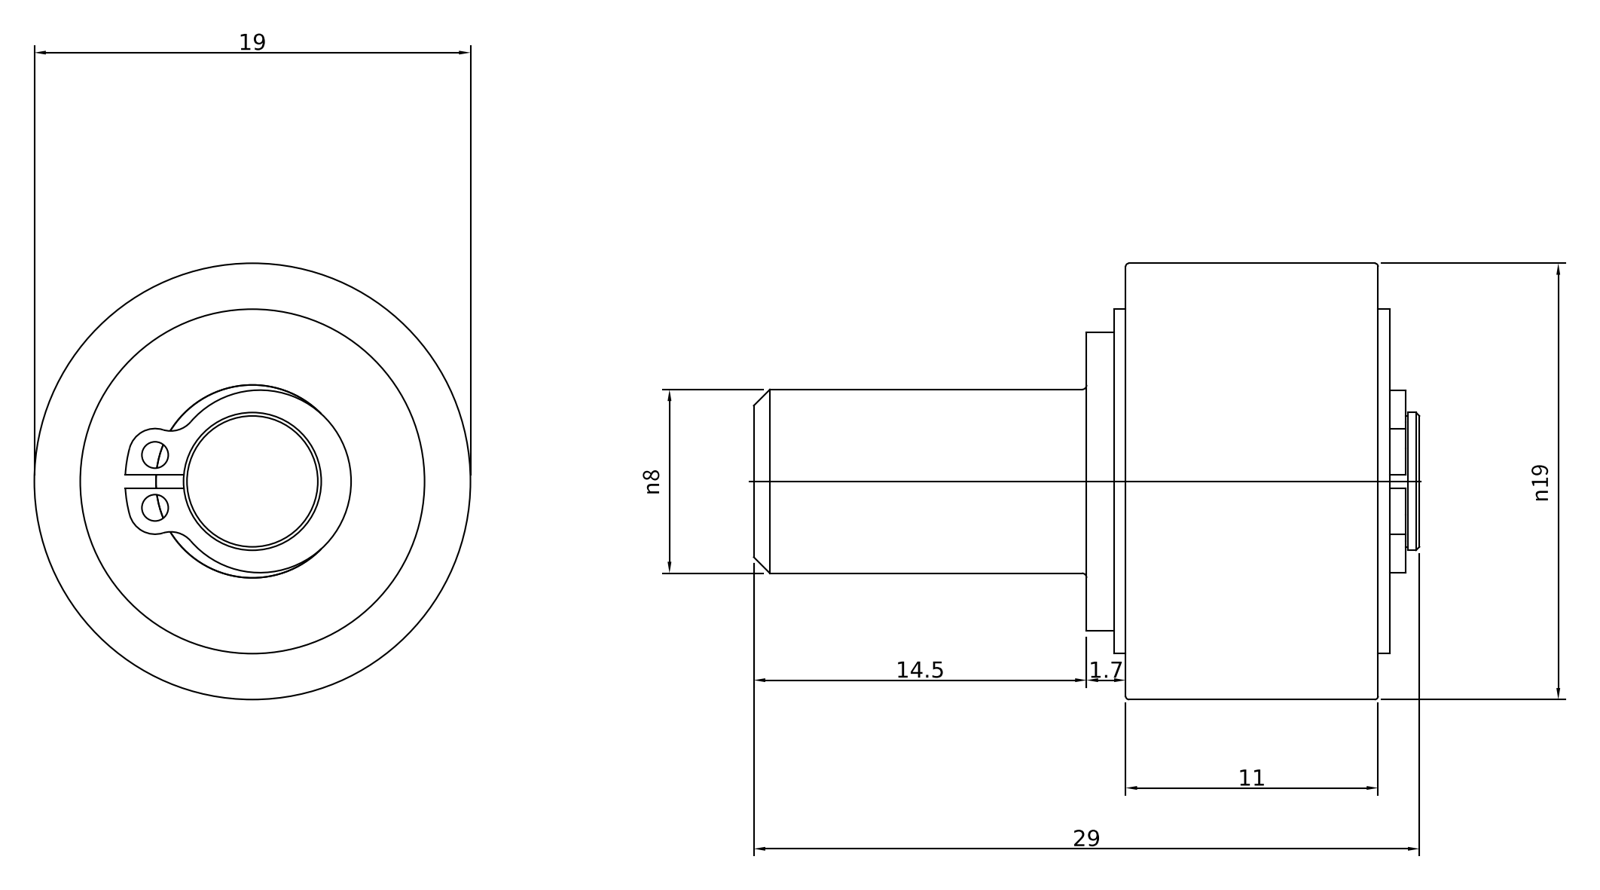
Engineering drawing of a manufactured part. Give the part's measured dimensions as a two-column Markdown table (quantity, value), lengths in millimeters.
| quantity | value |
| --- | --- |
| part name | DM23.519.00C; DM70PRR0022-A; DM80CUNATR6; 80AE00006 |
| STEP written by | Autodesk Inventor 2022 (AUTOMOTIVE_DESIGN) |
| units | millimeters |
| bodies | 3 solids, 56 faces (24 planar, 23 cylindrical, 9 other) |
| overall size | 29 × 19 × 19 |
| volume | 4 207 mm³ |
| surface area | 2 479 mm² |
| round holes (diameter × count) | 1.15 × 2, 5.7 × 1, 8.4 × 1 |
| round bosses / shafts (diameter × count) | 19 × 1, 15 × 1, 13 × 1, 8.4 × 1, 8 × 1, 6 × 1 |
| partial cylindrical surfaces (radius × count) | 1.15 × 4, 3.98 × 1, 5.54 × 1 |
| main face-to-face distances | 0.5, 11.5, 12, 1.2, 12.7, 11, 1.7, 13.2, 14.5, 13.9 |
| hole center spacings | 4.39, 2.3 |
